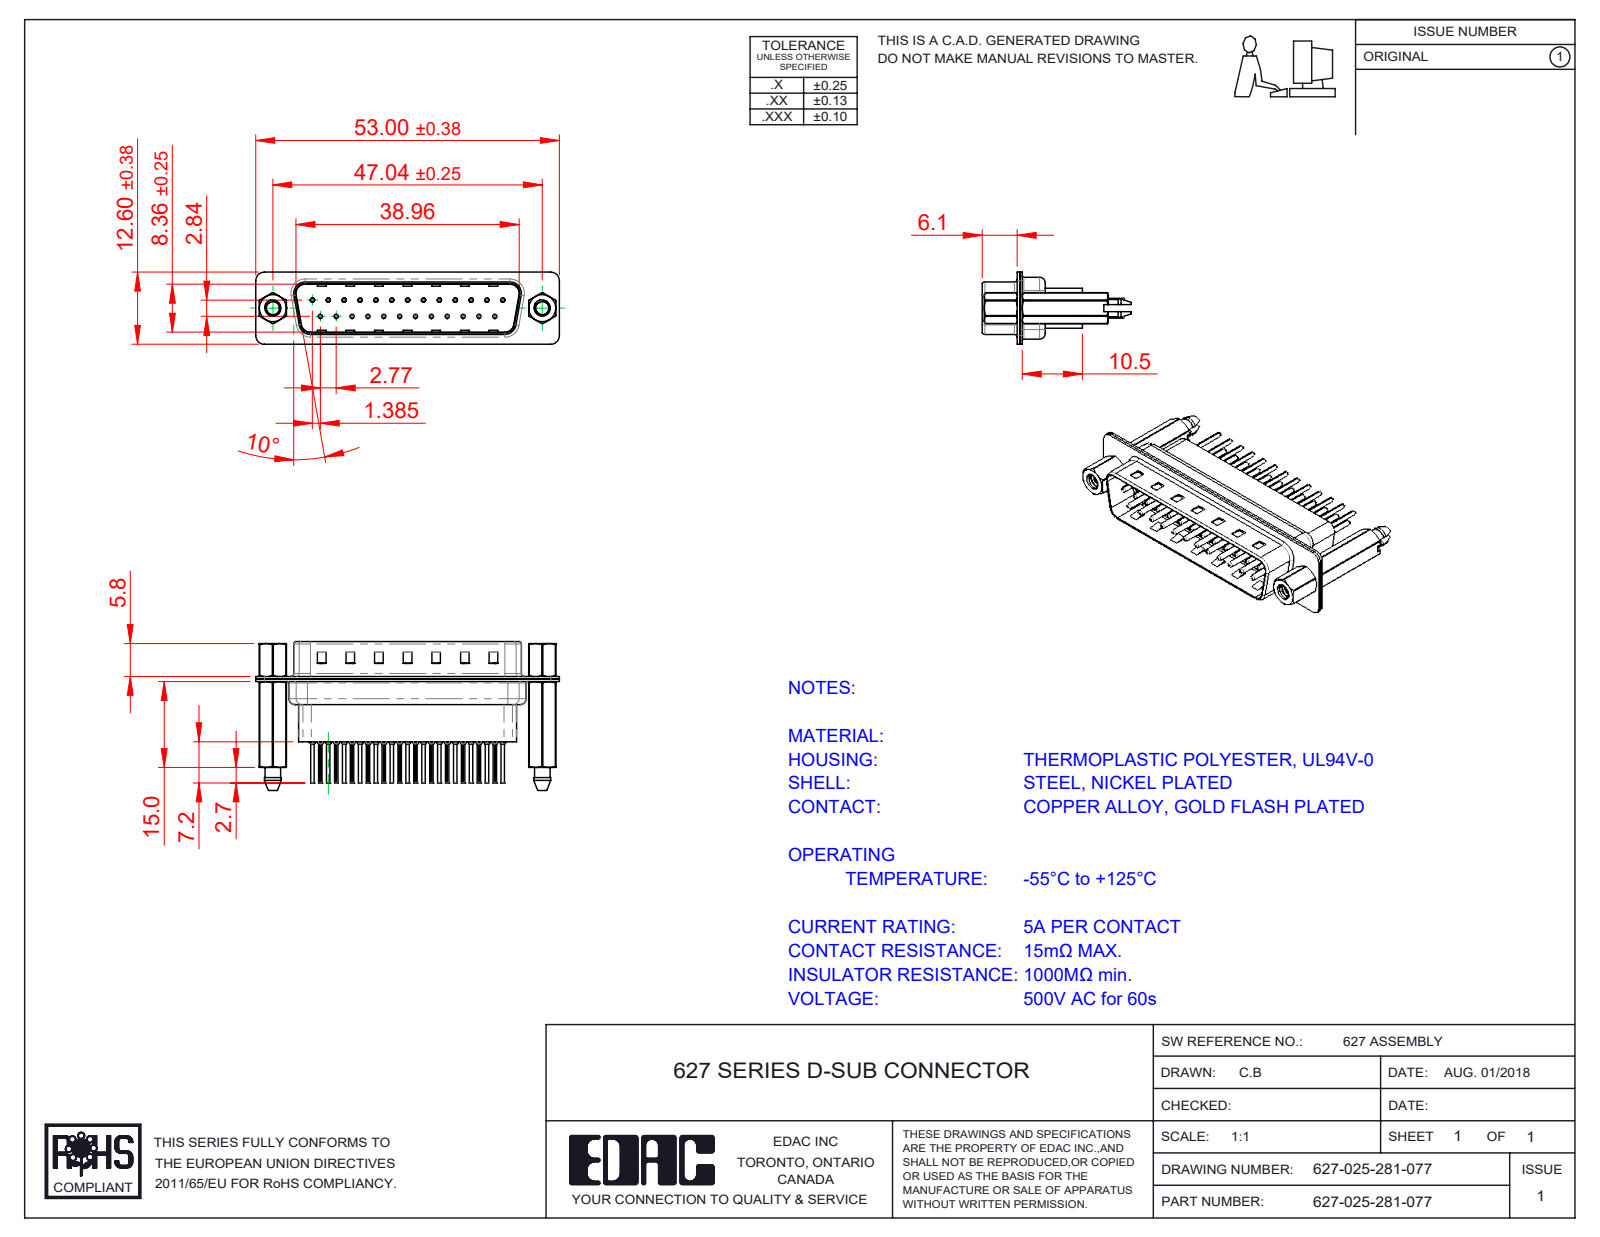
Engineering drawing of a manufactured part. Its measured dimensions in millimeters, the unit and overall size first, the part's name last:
Units: millimetres
Overall size (bounding box): 53 × 25.9 × 12.6
Round holes (diameter × count): ⌀0.2 ×25, ⌀0.35 ×25, ⌀1.1 ×25, ⌀1.6 ×25, ⌀2.26 ×2, ⌀2.29 ×2, ⌀4 ×2, ⌀4.8 ×2
Round bosses / shafts (diameter × count): ⌀2 ×25, ⌀1.5 ×25, ⌀0.75 ×25, ⌀0.6 ×25, ⌀4.9 ×2, ⌀2.79 ×2
Partial cylindrical surfaces — rounded edges, fillets, slot ends (radius × count): R0.1 ×50, R1.5 ×18, R2 ×12, R1.6 ×10, R0.5 ×8, R0.25 ×4, R0.6 ×4, R0.65 ×4
Main face-to-face distances: 0.4, 0.45, 0.82, 9.58, 0.68, 7.68, 1.5, 0.9, 1.08, 8.08
Hole centre spacings: 3.16, 8.31, 2.77, 5.54, 11.08, 16.62, 5.03, 5.04
Volume: 4 417 mm³ · Surface area: 11 314 mm²
Bodies: 32 solids, 3060 faces (825 planar, 1200 cylindrical, 1035 other)
Part name (STEP PRODUCT): 627 4-40 Threaded Boardlock_HP81; 627-025-281-077; 627 Contact Row 2_61; 627 Shell Rear_25 Contacts (+4 more)
STEP written by: SolidWorks 2020 (CONFIG_CONTROL_DESIGN)
